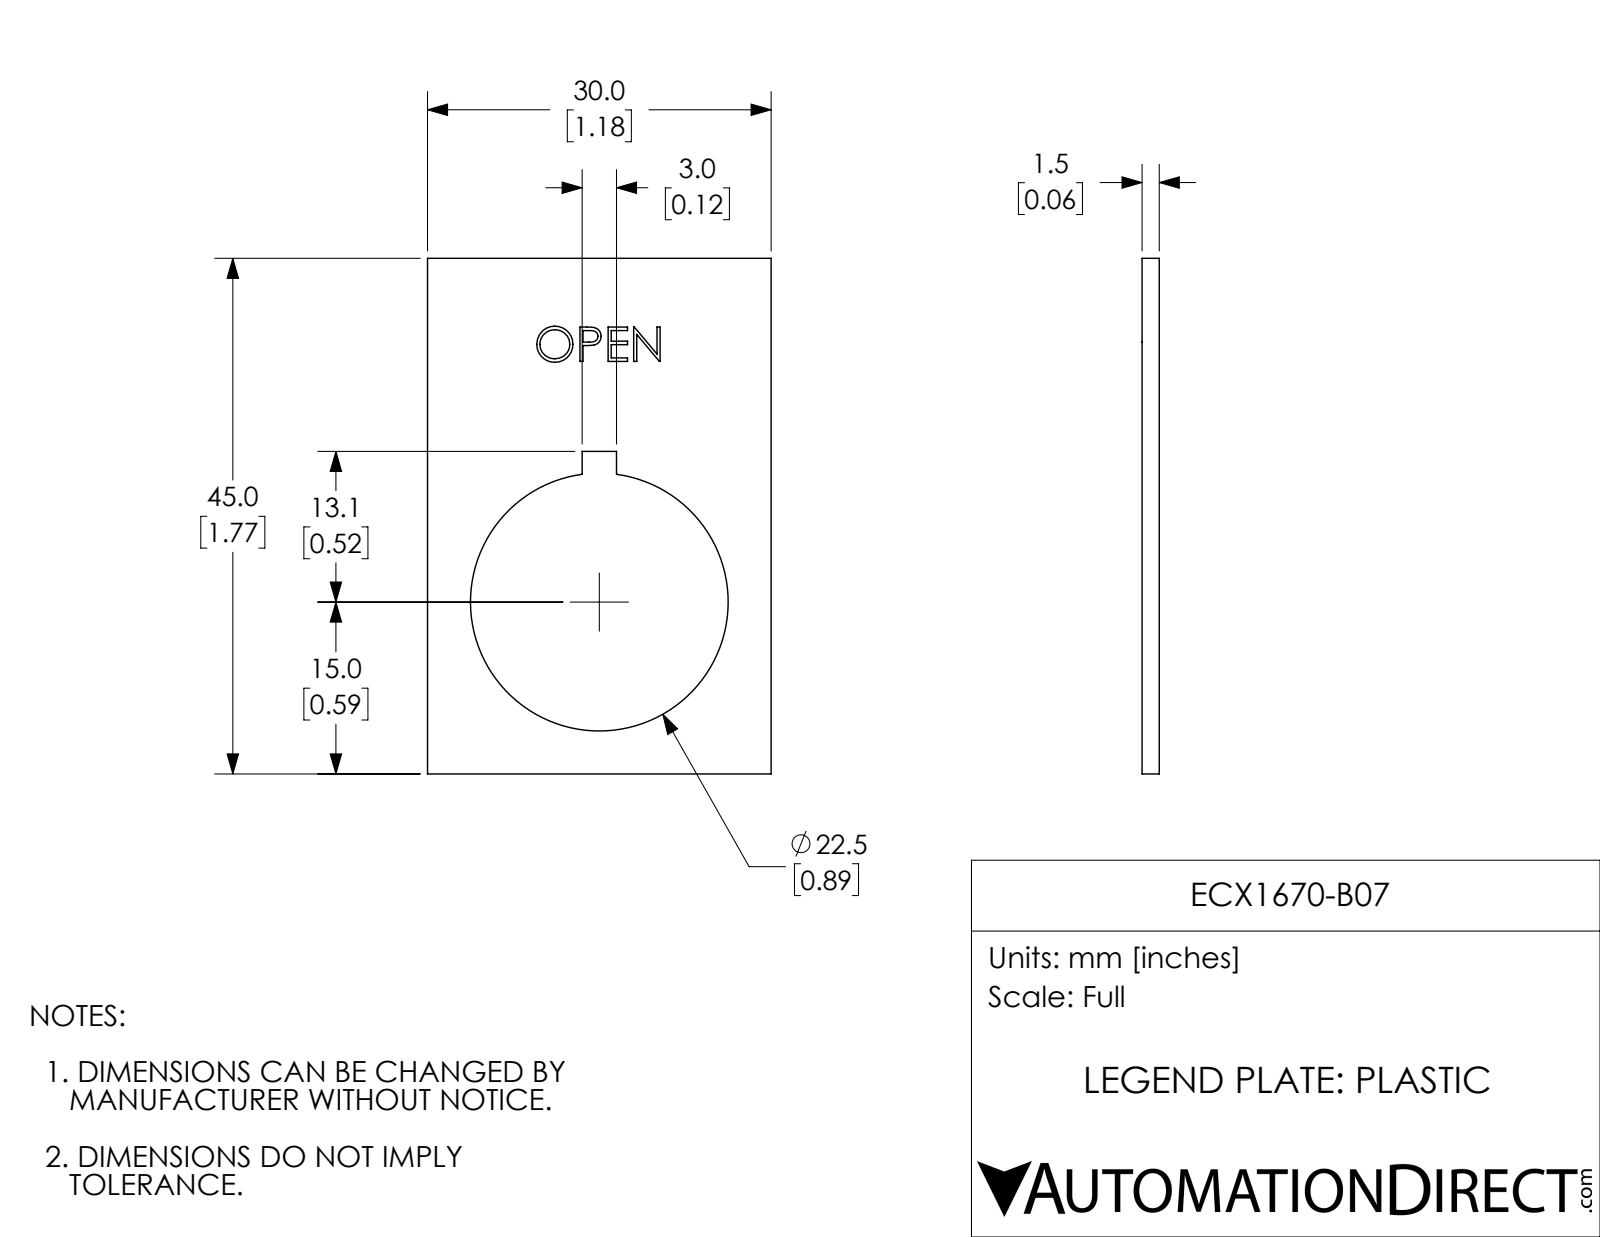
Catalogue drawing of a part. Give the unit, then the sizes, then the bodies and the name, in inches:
Units: inches
Overall size (bounding box): 1.772 × 1.181 × 0.059
Round holes (diameter × count): ⌀0.886 ×1
Main face-to-face distances: 0.059, 1.181, 1.772, 0.058, 0.531, 0.65, 1.108, 0.663, 0.118, 0.07
Volume: 0.087 in³ · Surface area: 3.459 in²
Bodies: 1 solid, 62 faces (45 planar, 3 cylindrical, 14 other)
Part name (STEP PRODUCT): ECX1670-B07
STEP written by: SolidWorks 2017 (AUTOMOTIVE_DESIGN)
